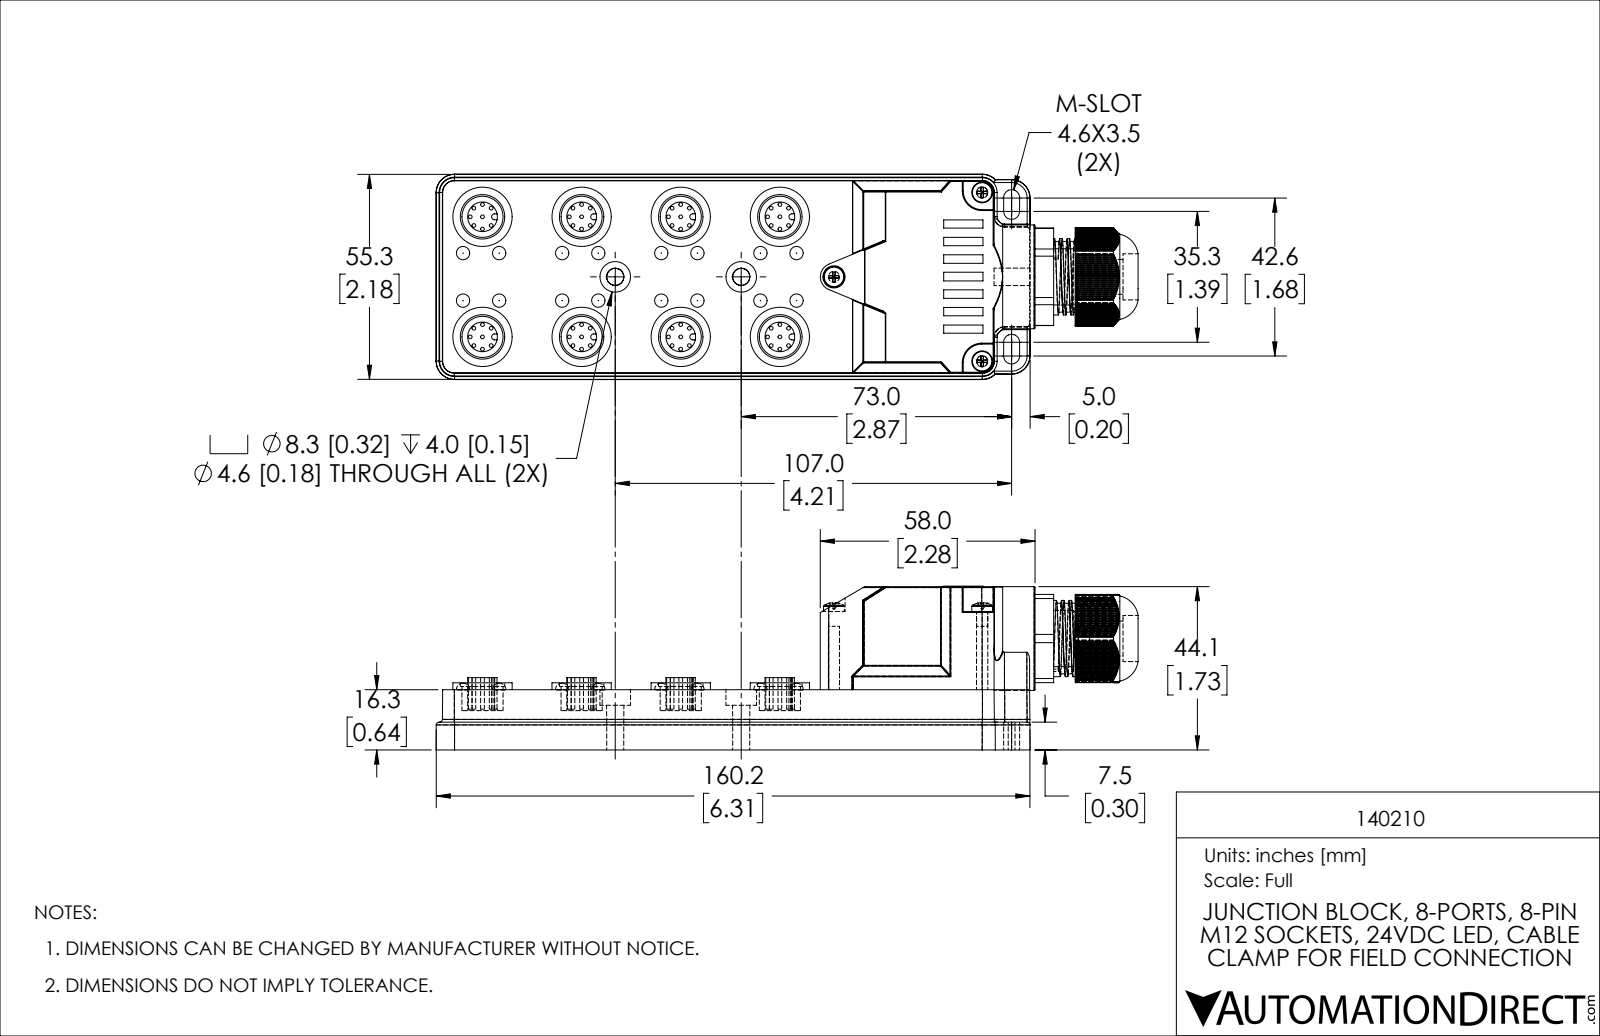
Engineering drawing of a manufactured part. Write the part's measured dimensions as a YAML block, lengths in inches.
part_name: "1402101_REV2"
step_written_by: "SolidWorks 2019 (AUTOMOTIVE_DESIGN)"
units: inches
bodies: {solids: 1, faces: 922, planar: 567, cylindrical: 233, other: 122}
overall_size: [7.566, 2.181, 1.739]
volume: 12.42
surface_area: 62.81
round_holes:
  - {diameter: 0.039, count: 64}
  - {diameter: 0.437, count: 8}
  - {diameter: 0.472, count: 8}
  - {diameter: 0.181, count: 2}
  - {diameter: 0.325, count: 2}
  - {diameter: 0.236, count: 1}
  - {diameter: 0.49, count: 1}
round_bosses_or_shafts:
  - {diameter: 0.142, count: 16}
  - {diameter: 0.63, count: 8}
  - {diameter: 0.315, count: 6}
  - {diameter: 0.315, count: 2}
  - {diameter: 1.102, count: 1}
  - {diameter: 0.837, count: 1}
partial_cylinders:
  - {radius: 0.01, count: 50}
  - {radius: 0.03, count: 16}
  - {radius: 0.031, count: 8}
  - {radius: 0.089, count: 4}
  - {radius: 0.11, count: 2}
  - {radius: 0.127, count: 2}
  - {radius: 0.197, count: 2}
  - {radius: 0.01, count: 1}
face_to_face_distances: [0.64, 0.065, 1.734, 1.094, 0.713, 0.073, 1.021, 0.112, 1.933, 0.295]
hole_center_spacings: [0.13, 1.053, 0.184, 1.275, 2.106, 1.148, 2.2, 1.654]
